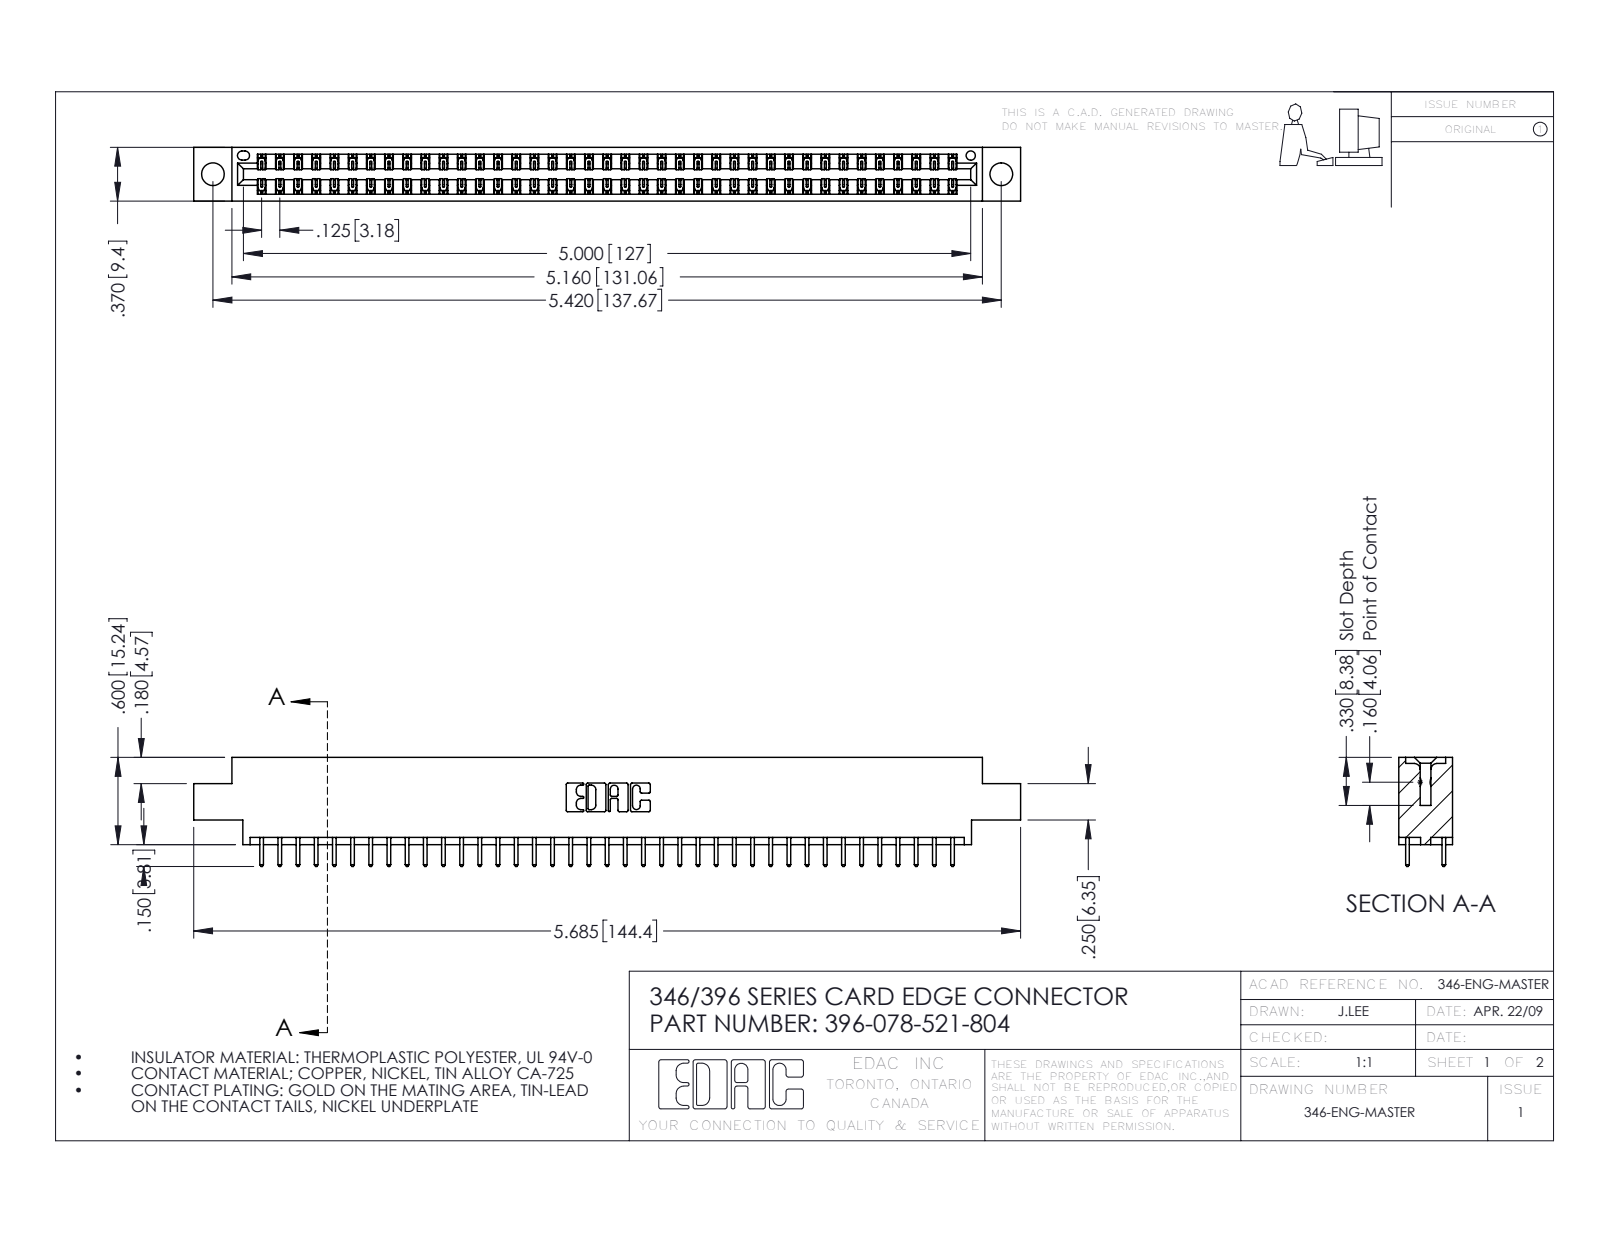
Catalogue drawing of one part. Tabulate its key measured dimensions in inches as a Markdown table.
| quantity | value |
| --- | --- |
| part name | 346 Part_0.170 Offset - 0.156 Dia-TH; 396-078-521-804; 345-292-001_345-293-121 |
| STEP written by | SolidWorks 2016 (CONFIG_CONTROL_DESIGN) |
| units | inches |
| bodies | 79 solids, 4182 faces (2810 planar, 1372 cylindrical, 0 other) |
| overall size | 5.685 × 0.75 × 0.37 |
| volume | 0.841 in³ |
| surface area | 28.95 in² |
| round holes (diameter × count) | 0.156 × 2, 0.064 × 1 |
| partial cylindrical surfaces (radius × count) | 0.006 × 117, 0.01 × 78, 0.01 × 22, 0.007 × 6, 0.031 × 6, 0.026 × 3, 0.014 × 2, 0.022 × 2 |
| main face-to-face distances | 0.048, 0.322, 0.37, 0.25, 0.072, 0.298, 0.025, 0.275, 0.148, 0.222 |
| hole center spacings | 0.246, 5.211, 5.42 |
